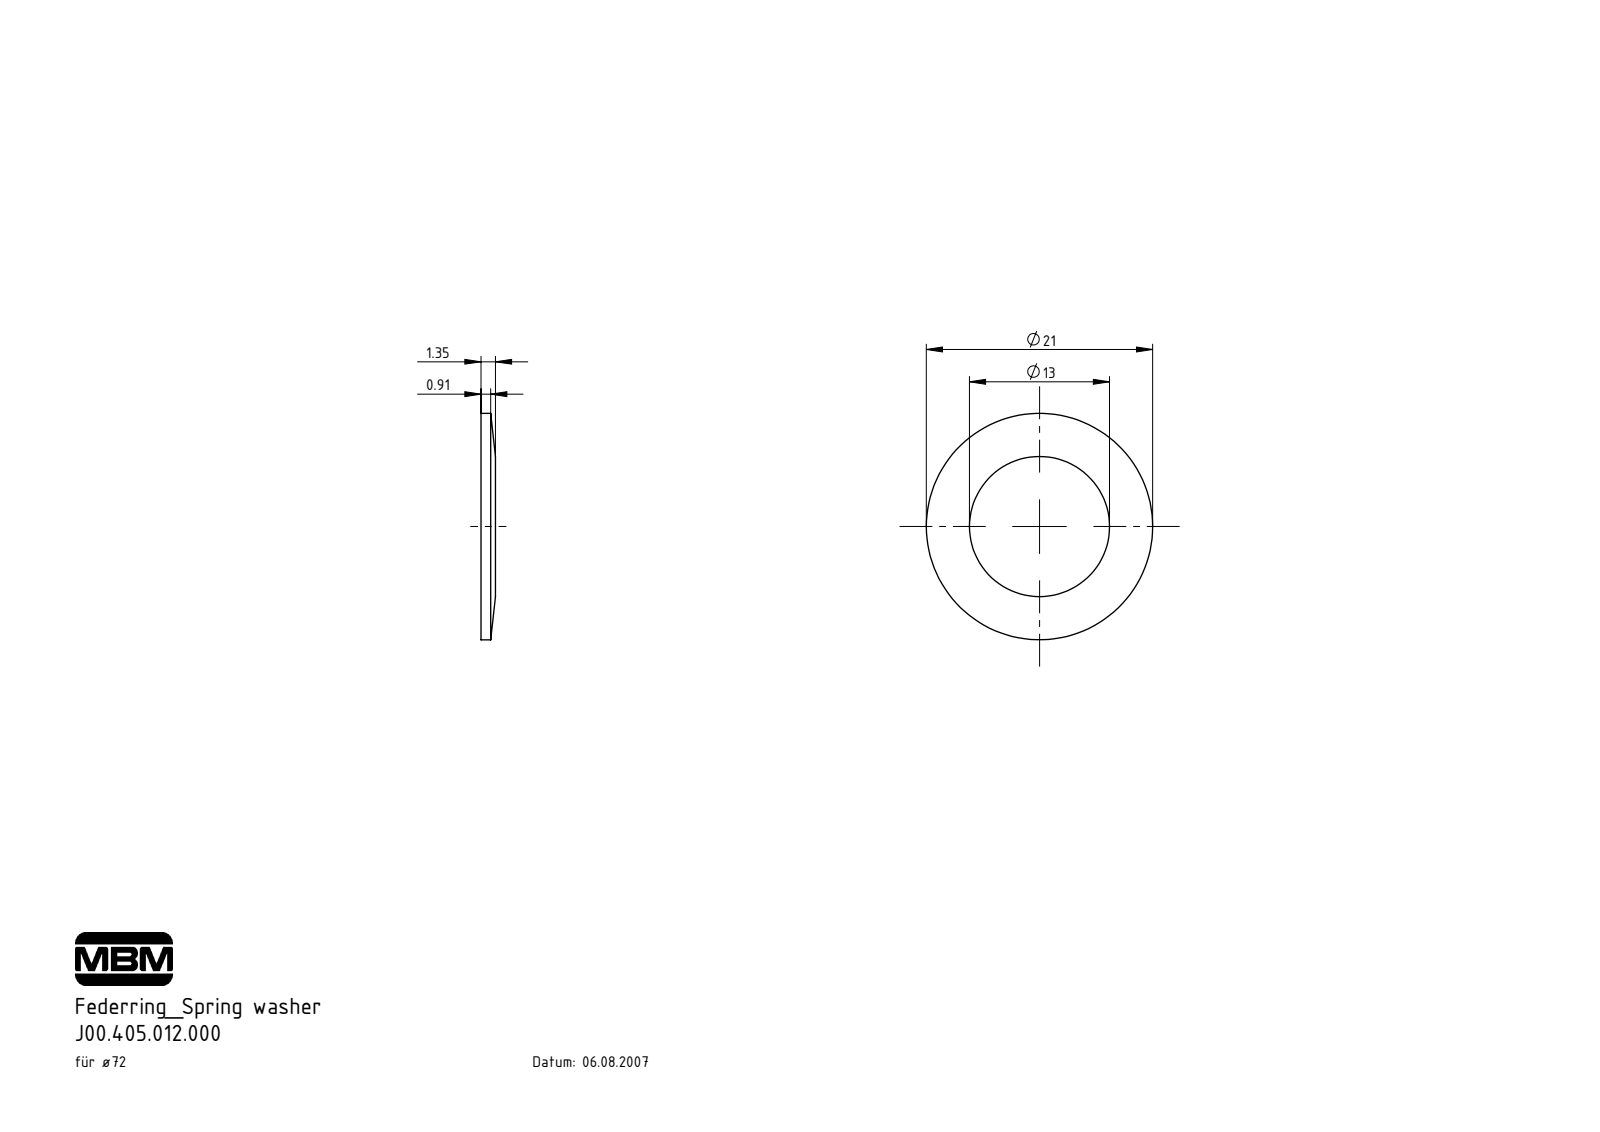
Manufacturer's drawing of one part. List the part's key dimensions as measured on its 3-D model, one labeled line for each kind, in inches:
Part name (STEP PRODUCT): J00.405.012.000
STEP written by: SolidWorks 2022 (AUTOMOTIVE_DESIGN)
Units: inches
Bodies: 1 solid, 6 faces (2 planar, 4 cylindrical, 0 other)
Overall size (bounding box): 0.827 × 0.827 × 0.035
Volume: 0.012 in³ · Surface area: 0.811 in²
Round holes (diameter × count): ⌀0.512 ×1
Round bosses / shafts (diameter × count): ⌀0.827 ×1
Main face-to-face distances: 0.035
